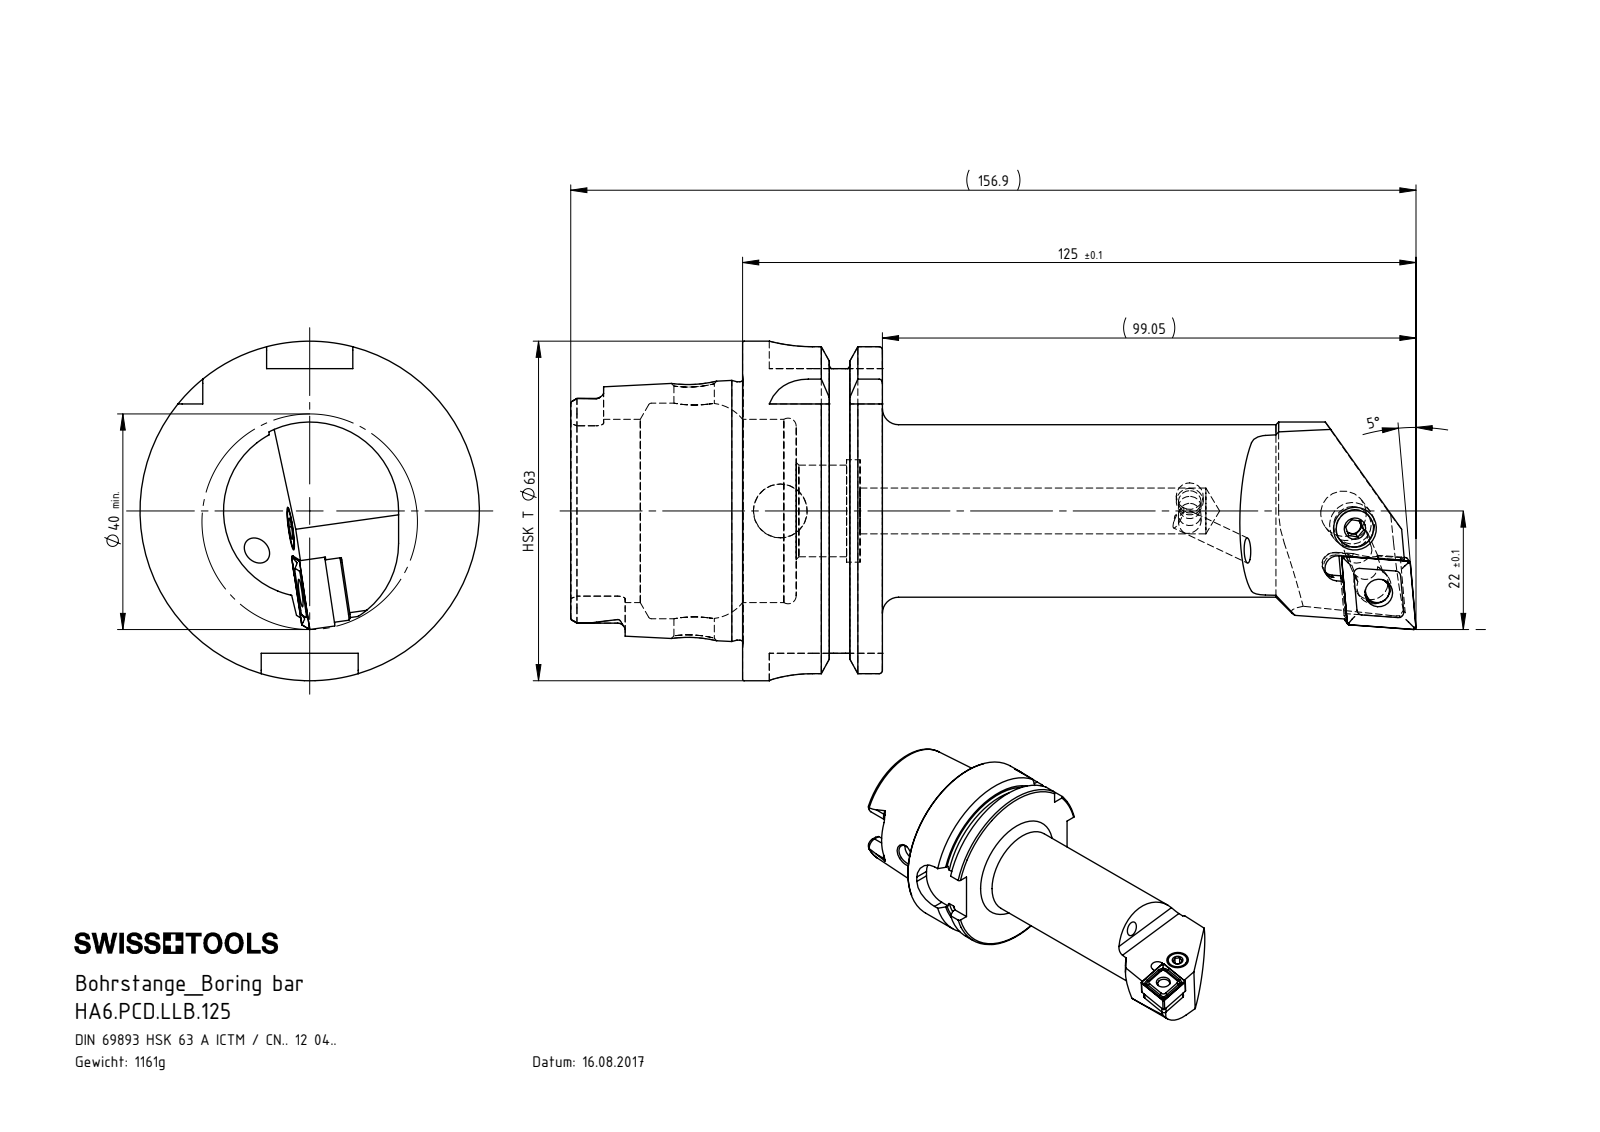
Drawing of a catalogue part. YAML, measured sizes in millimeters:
part_name: "KVT_MB_600_050; CNMG120404; HA6-PCD.LLB.125_A; WCD-ER4.101.017_A (+4 more)"
step_written_by: "SolidWorks 2017 (CONFIG_CONTROL_DESIGN)"
units: millimeters
bodies: {solids: 7, faces: 364, planar: 115, cylindrical: 104, other: 145}
overall_size: [156.9, 63, 63]
volume: 147122
surface_area: 36295
round_holes:
  - {diameter: 4.2, count: 2}
  - {diameter: 4, count: 1}
  - {diameter: 5, count: 1}
  - {diameter: 5.16, count: 1}
  - {diameter: 6.4, count: 1}
  - {diameter: 7, count: 1}
  - {diameter: 7.5, count: 1}
  - {diameter: 8.4, count: 1}
  - {diameter: 8.5, count: 1}
  - {diameter: 10, count: 1}
  - {diameter: 17, count: 1}
  - {diameter: 19, count: 1}
round_bosses_or_shafts:
  - {diameter: 63, count: 1}
  - {diameter: 54.95, count: 1}
  - {diameter: 47.94, count: 1}
  - {diameter: 32, count: 1}
  - {diameter: 8, count: 1}
  - {diameter: 7.9, count: 1}
  - {diameter: 6.4, count: 1}
  - {diameter: 5, count: 1}
partial_cylinders:
  - {radius: 1.4, count: 6}
  - {radius: 0.4, count: 4}
  - {radius: 1, count: 4}
  - {radius: 8, count: 4}
  - {radius: 2.5, count: 2}
  - {radius: 2.82, count: 2}
  - {radius: 2.88, count: 2}
  - {radius: 2.1, count: 1}
face_to_face_distances: [25.95, 16, 9.95, 31.9, 41.85, 57.85, 52.8, 21.8, 11.85, 4.49]
hole_center_spacings: [12.8, 12.87]
